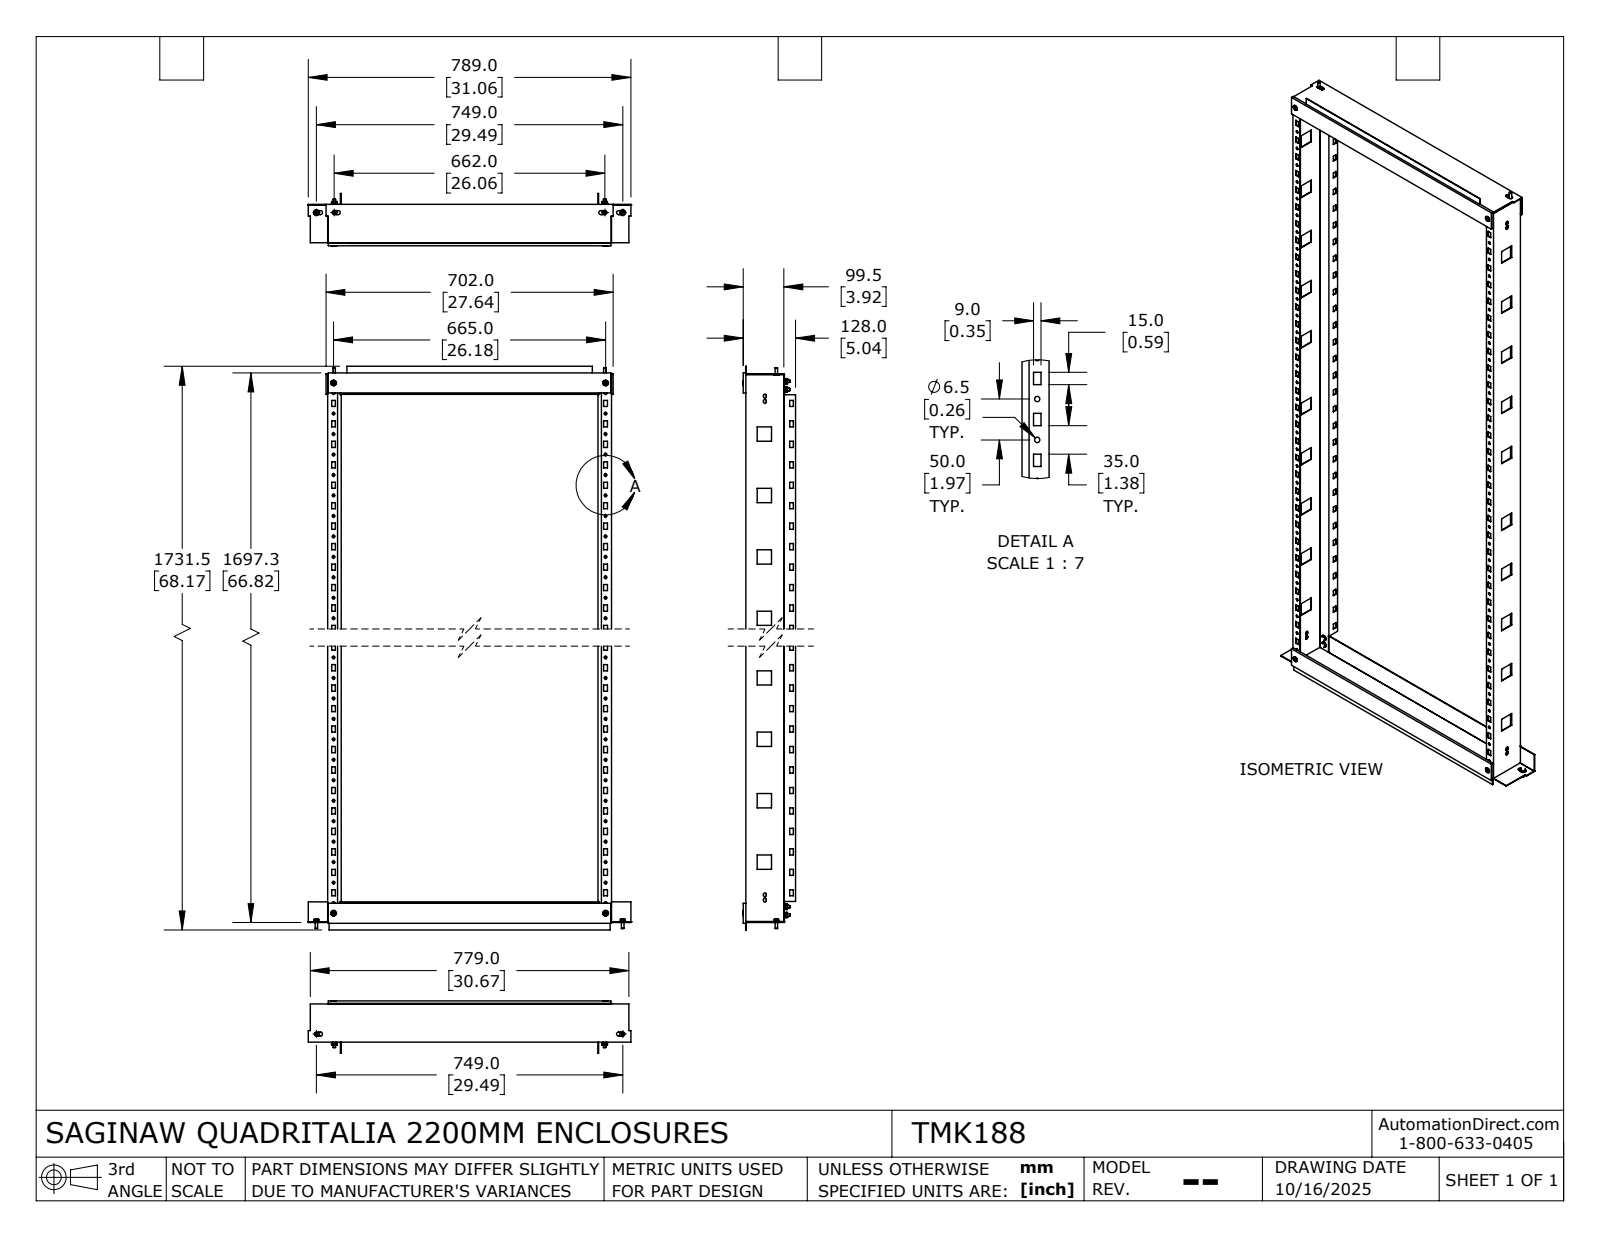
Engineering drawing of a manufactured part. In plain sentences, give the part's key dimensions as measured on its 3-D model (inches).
The part is named "TMK188". Its 3-D file was written by "SolidWorks 2024 (AUTOMOTIVE_DESIGN)". It is 1 solid with 2322 faces: 1560 planar, 622 cylindrical and 140 other. Overall it measures 68.169 by 31.063 by 5.051 inches. Its volume is 80.12 cubic inches and its surface area 2 732 square inches. Round holes: 66 of diameter 0.256, 8 of diameter 0.276, 4 of diameter 0.156. Round bosses or shafts: 16 of diameter 0.236, 12 of diameter 0.551, 4 of diameter 0.472, 4 of diameter 0.394. Partial cylindrical surfaces (rounded edges, fillets, slot ends): 96 of radius 0.01, 80 of radius 0.02, 32 of radius 0.039, 24 of radius 0.138, 16 of radius 0.177, 8 of radius 0.197. The main face-to-face distances are 0.059, 27.264, 1.24, 26.024, 27.323, 27.205, 3.602, 3.661, 0.256, 3.917. The hole center spacings are 3.937, 1.969, 5.906, 7.874, 9.843, 11.811, 13.78, 15.748.
